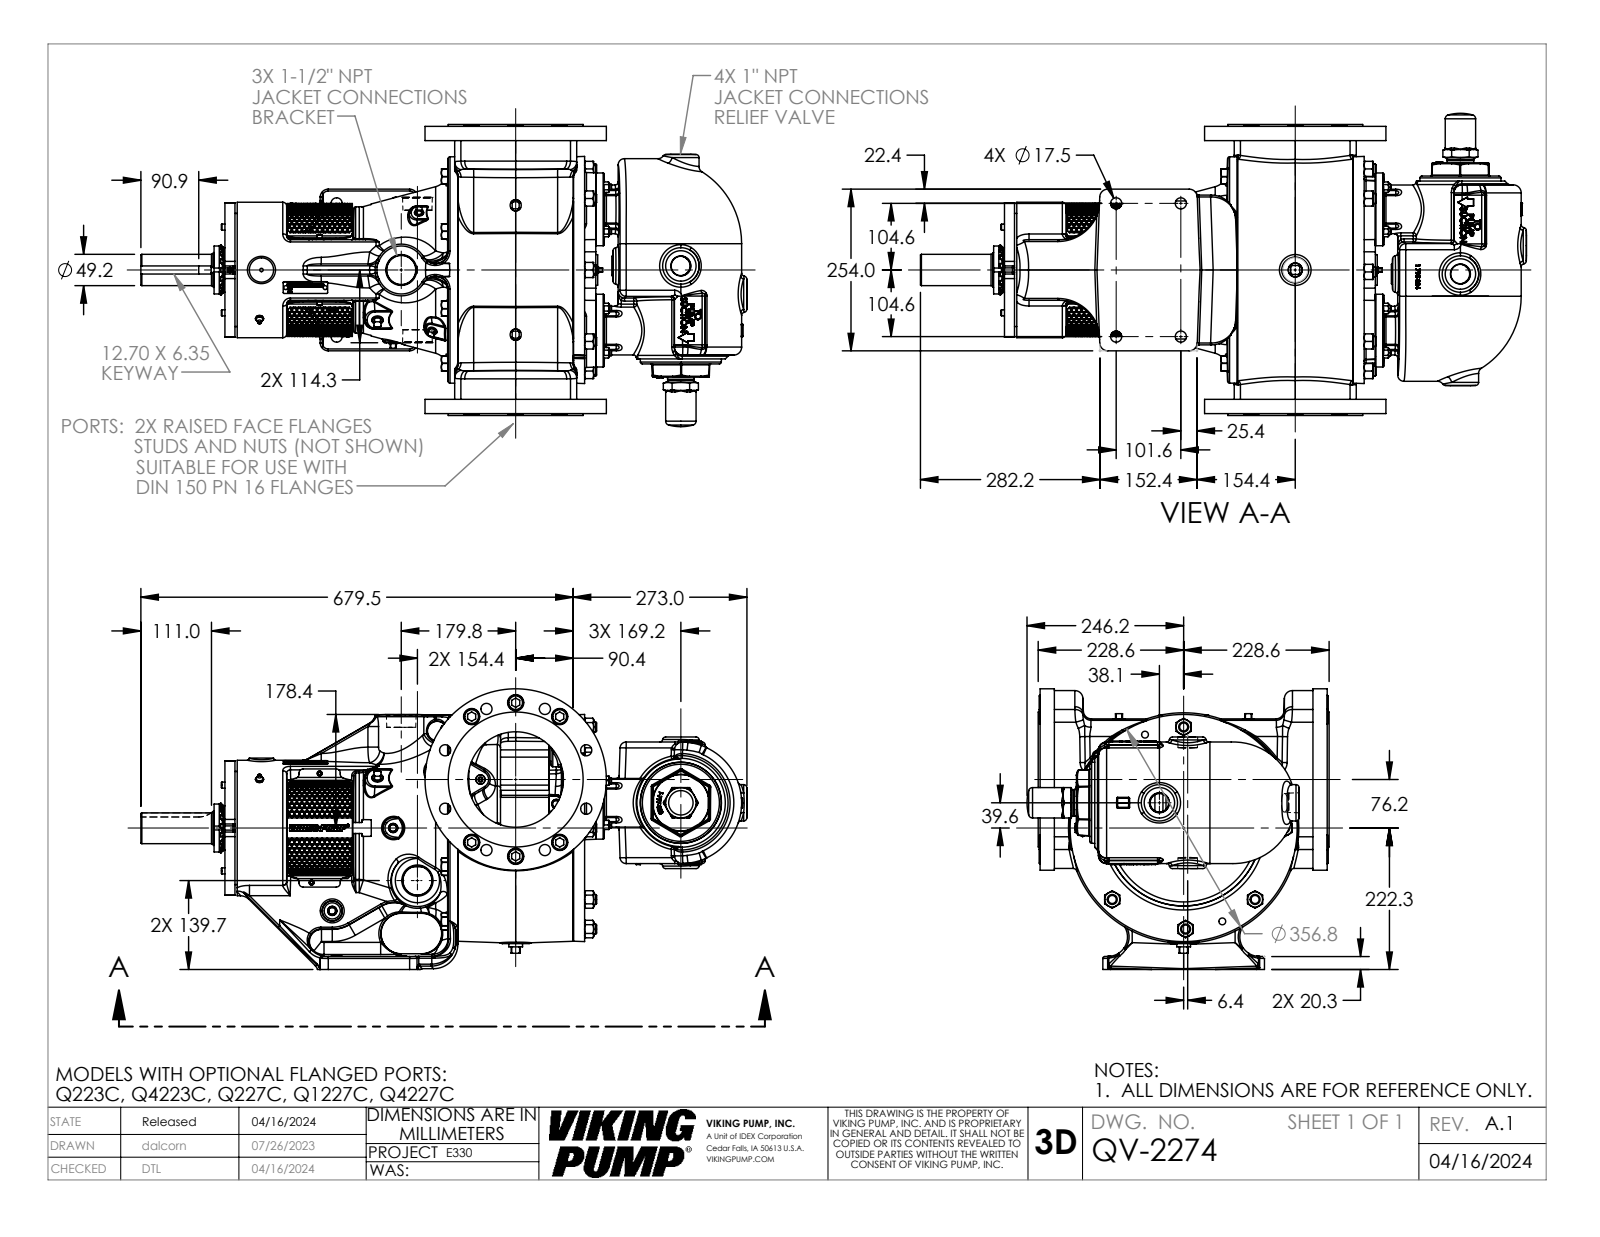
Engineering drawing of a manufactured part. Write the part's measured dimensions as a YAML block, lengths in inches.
part_name: "QV-2274"
step_written_by: "SolidWorks 2022 (AUTOMOTIVE_DESIGN)"
units: inches
bodies: {solids: 1, faces: 8091, planar: 2779, cylindrical: 779, other: 4533}
overall_size: [37.499, 18.692, 17.36]
volume: 3149
surface_area: 2641
round_holes:
  - {diameter: 0.689, count: 8}
  - {diameter: 1.157, count: 8}
  - {diameter: 0.656, count: 6}
  - {diameter: 1, count: 6}
  - {diameter: 0.688, count: 4}
  - {diameter: 0.159, count: 2}
  - {diameter: 0.313, count: 2}
  - {diameter: 0.33, count: 2}
  - {diameter: 0.453, count: 1}
  - {diameter: 2.157, count: 1}
  - {diameter: 2.167, count: 1}
  - {diameter: 2.182, count: 1}
round_bosses_or_shafts:
  - {diameter: 0.617, count: 8}
  - {diameter: 0.369, count: 8}
  - {diameter: 0.937, count: 6}
  - {diameter: 0.625, count: 4}
  - {diameter: 0.625, count: 3}
  - {diameter: 0.437, count: 3}
  - {diameter: 0.312, count: 3}
  - {diameter: 4.5, count: 2}
partial_cylinders:
  - {radius: 0.12, count: 52}
  - {radius: 0.19, count: 44}
  - {radius: 0.5, count: 26}
  - {radius: 0.03, count: 25}
  - {radius: 0.06, count: 22}
  - {radius: 0.015, count: 18}
  - {radius: 0.092, count: 18}
  - {radius: 0.25, count: 18}
face_to_face_distances: [1, 17, 18, 16, 3.75, 0.5, 22.256, 21.756, 18.006, 18.506]
hole_center_spacings: [6.25, 8.839, 11.549, 4.724, 4.75, 6.681, 8.73, 9.418]
